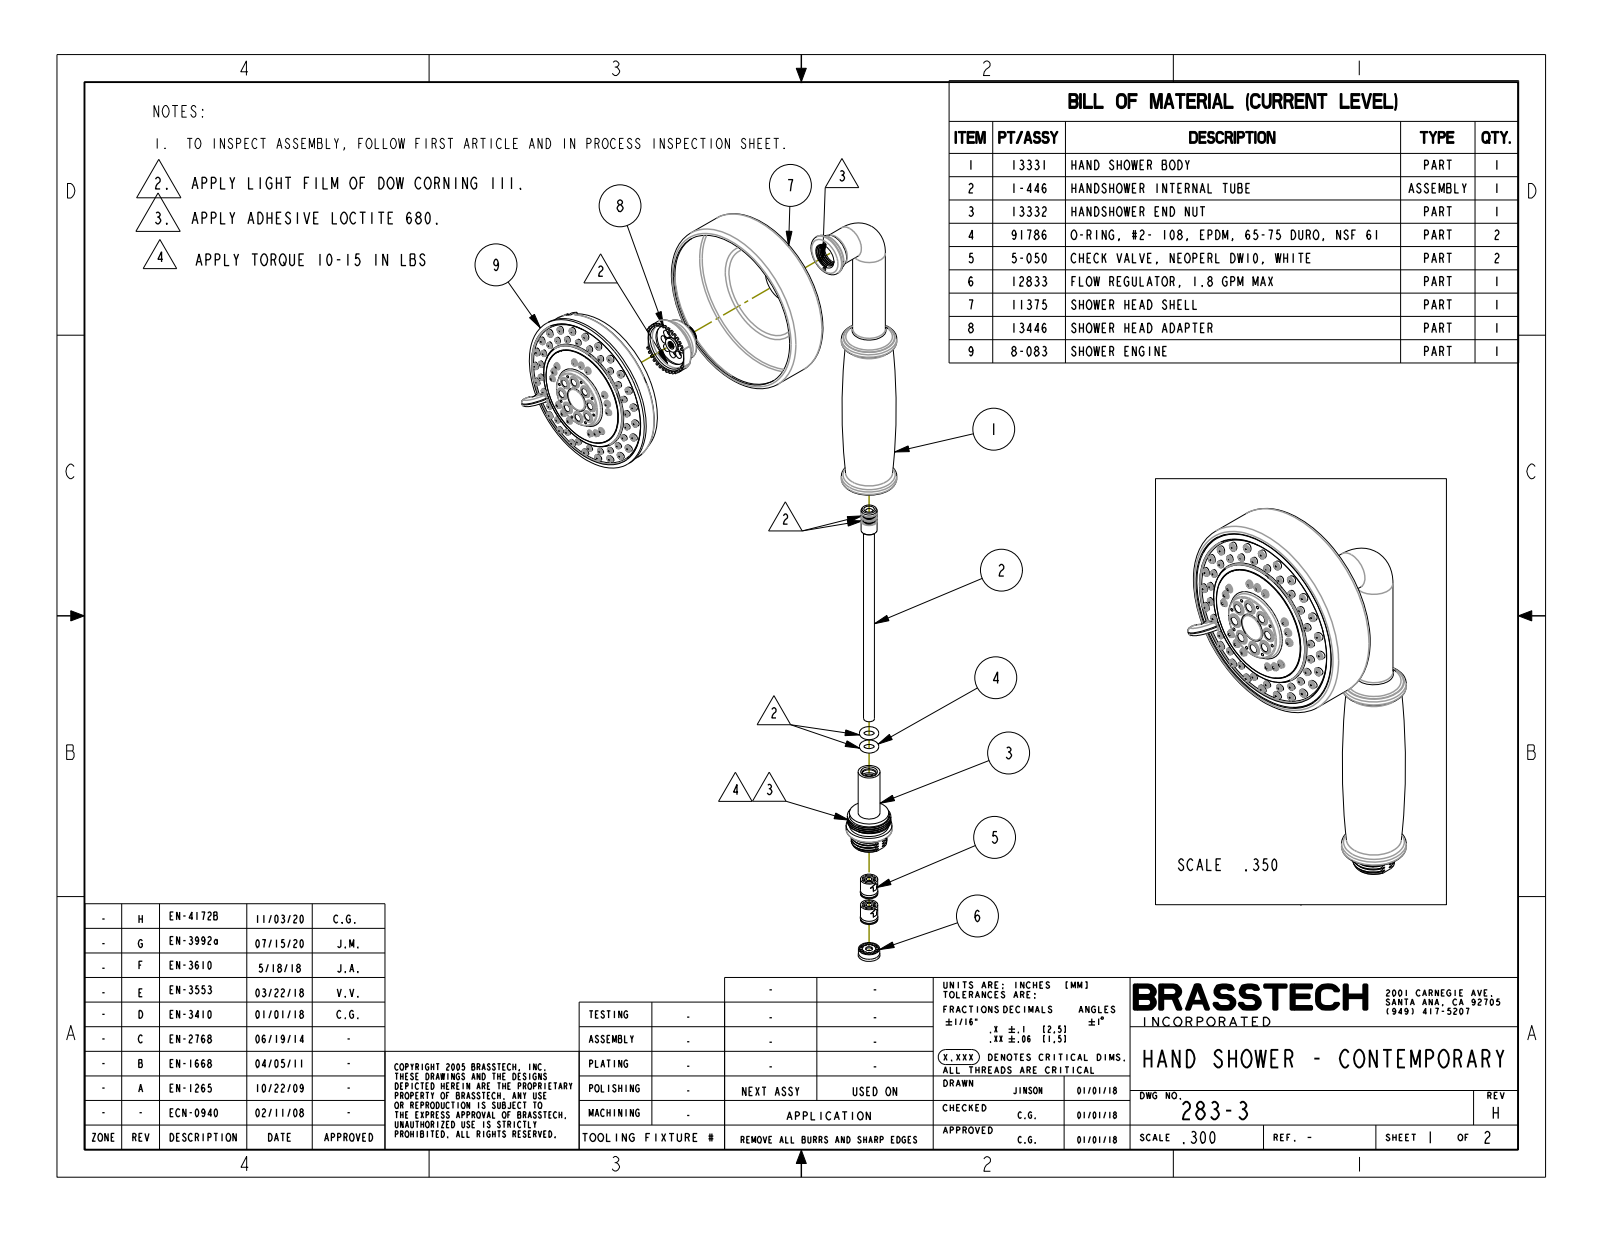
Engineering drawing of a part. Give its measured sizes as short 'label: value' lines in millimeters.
name: 13331; 11375; 283-3_ASM
written by: CREO PARAMETRIC BY PTC INC, 2018400 (CONFIG_CONTROL_DESIGN)
unit: mm
bodies: 2 solids, 1062 faces (123 planar, 180 cylindrical, 759 other)
size: 237.6 × 102.7 × 101.6
volume: 358 200 mm³; area: 46 790 mm²
holes: 8× ⌀1.5, 1× ⌀27.4
bosses: 39× ⌀3.6, 23× ⌀4.2, 2× ⌀19.1, 1× ⌀101.6, 1× ⌀59, 1× ⌀32.3, 1× ⌀26.7, 1× ⌀24.6
rounds: 4× R0.5, 1× R3.5, 1× R8, 1× R10.4, 1× R12, 1× R13, 1× R47.3
face distances: 15.8, 49.6, 33.8, 9.4, 3.2, 46.6, 30.8, 3, 9.3, 43.4
hole spacings: 11.3, 20.8, 27.2, 29.4
